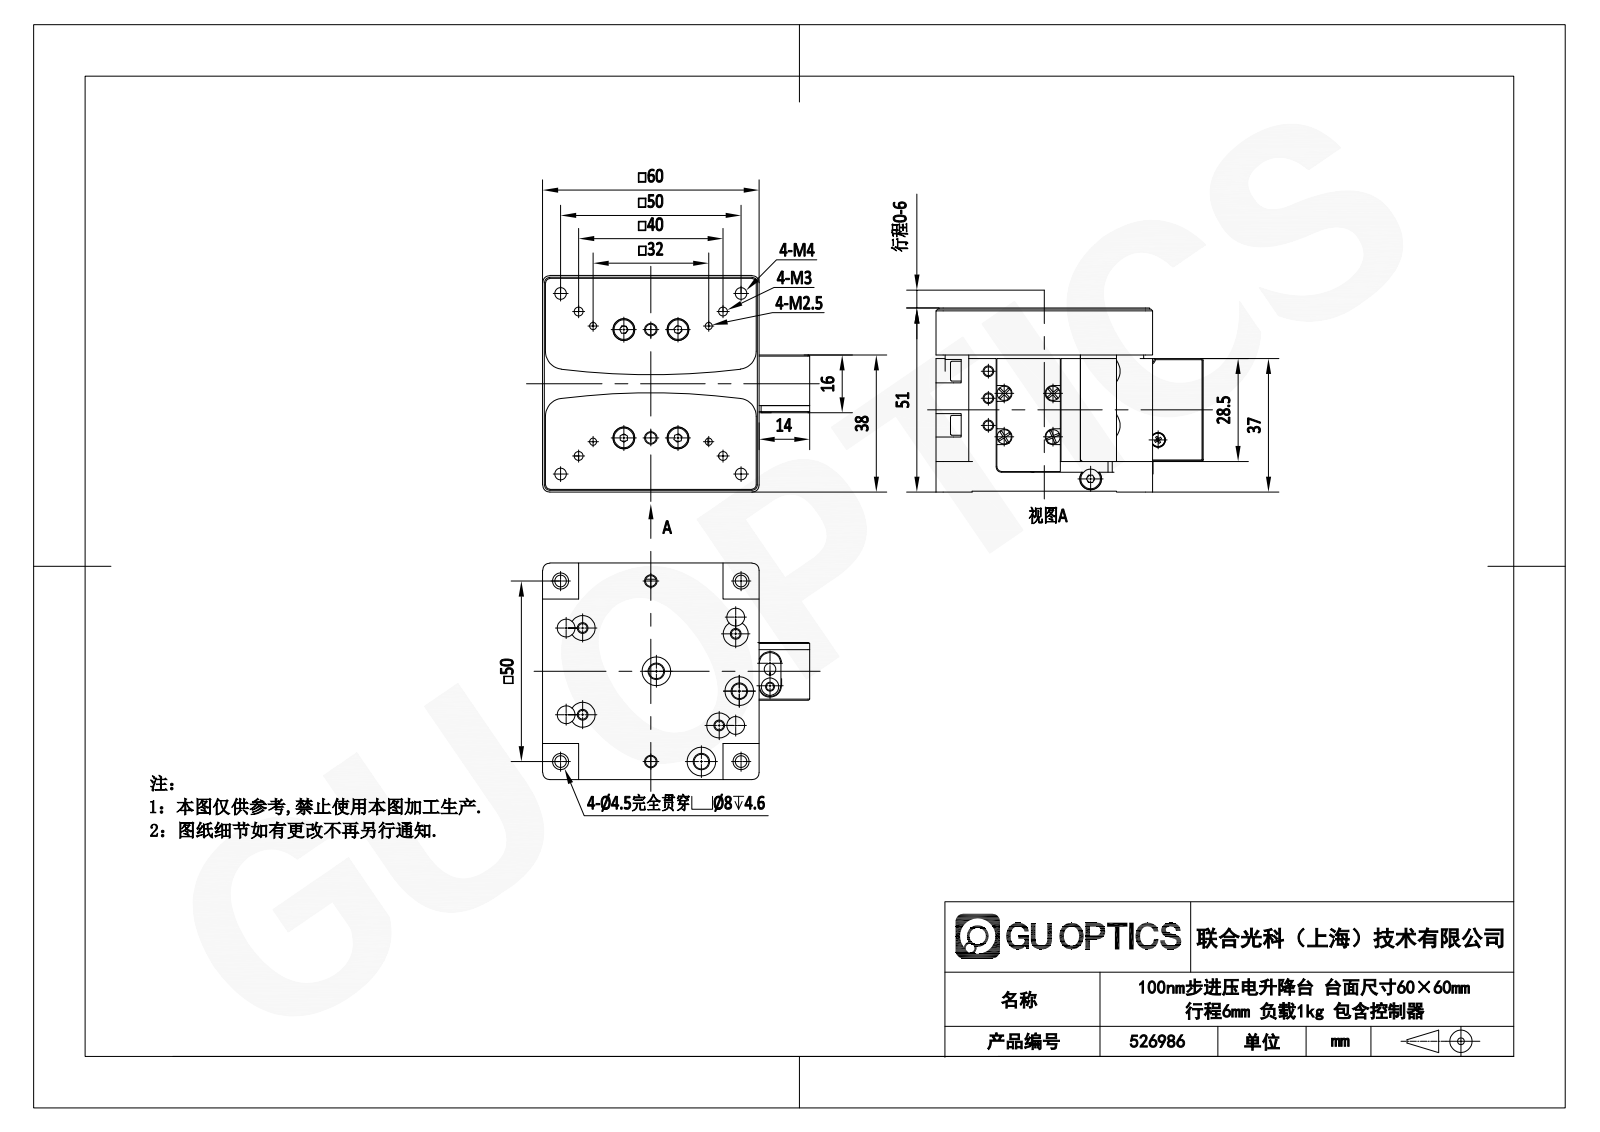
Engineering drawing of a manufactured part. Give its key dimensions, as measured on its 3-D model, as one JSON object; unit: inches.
{"part_name": "526963", "step_written_by": "SolidWorks 2020 (CONFIG_CONTROL_DESIGN)", "units": "inches", "bodies": {"solids": 0, "faces": 679, "planar": 332, "cylindrical": 249, "other": 98}, "overall_size": [3.659, 2.362, 2.008], "round_holes": [[0.157, 6], [0.165, 2], [0.161, 1]], "round_bosses_or_shafts": [[0.098, 12], [0.315, 7], [0.218, 5], [0.217, 5], [0.13, 5], [0.118, 5], [0.276, 4], [0.24, 4]], "partial_cylinders_radius": [[0.039, 16], [0.059, 7], [0.118, 6], [0.197, 6], [0.071, 5], [0.02, 4], [0.047, 4], [0.079, 4]], "face_to_face_distances": [1.417, 0.256, 2.362, 1.996, 1.74, 1.496, 1.673, 0.323, 0.079, 0.866], "hole_center_spacings": [0.472, 0.531, 0.711, 0.32, 0.591, 0.784, 1.146, 1.252]}
